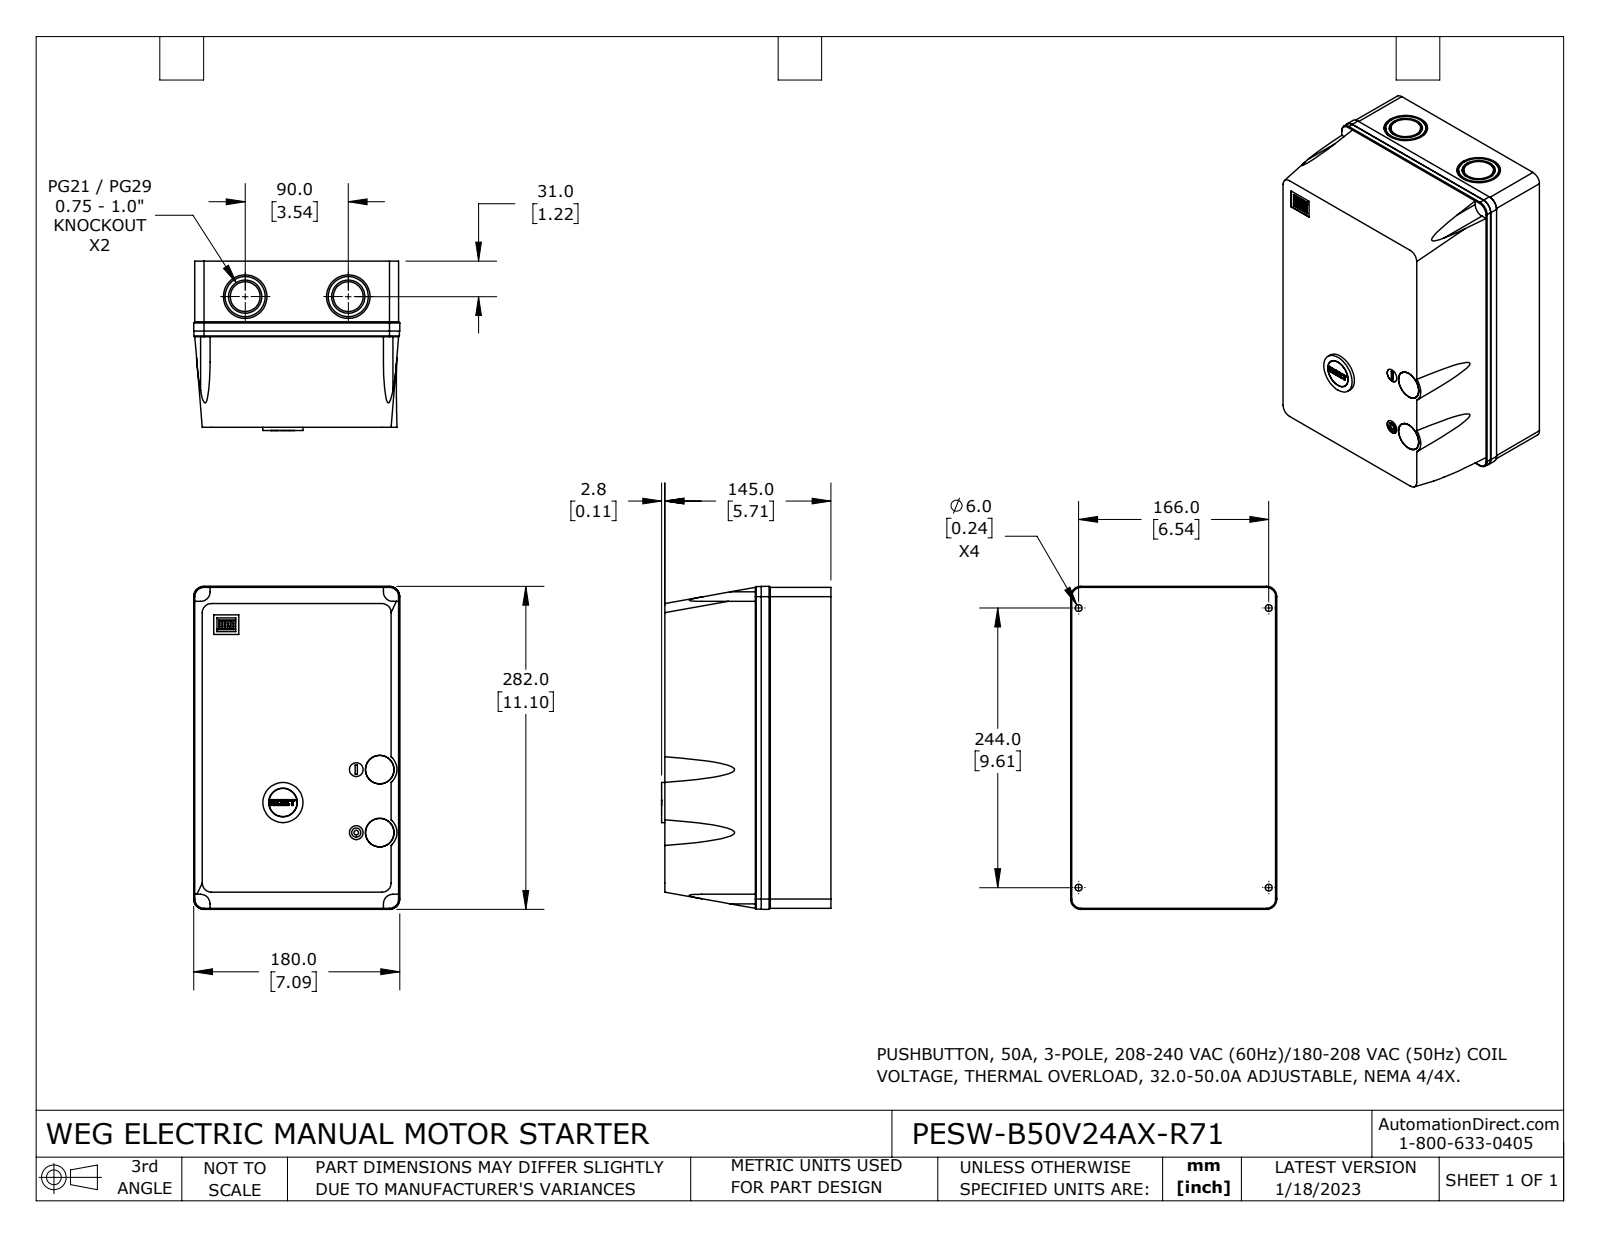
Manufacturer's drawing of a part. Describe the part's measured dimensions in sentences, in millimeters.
The part is named "PESW-B50V24AX-R71". Its 3-D file was written by "SolidWorks 2021 (CONFIG_CONTROL_DESIGN)". It is 3 solids with 286 faces: 130 planar, 144 cylindrical and 12 other. Overall it measures 282 by 180 by 147.9 millimeters. Its volume is 7 014 000 cubic millimeters and its surface area 232 257 square millimeters. Round holes: 4 of diameter 6, 3 of diameter 25, 2 of diameter 12, 2 of diameter 29, 2 of diameter 38, 1 of diameter 4, 1 of diameter 30.5. Round bosses or shafts: 3 of diameter 35, 2 of diameter 26, 2 of diameter 24.8, 1 of diameter 30.3, 1 of diameter 24.6, 1 of diameter 14, 1 of diameter 8. Partial cylindrical surfaces (rounded edges, fillets, slot ends): 34 of radius 0.1, 4 of radius 8, 4 of radius 8.3, 4 of radius 8.7, 4 of radius 9, 1 of radius 1.6. The main face-to-face distances are 145, 178, 280, 1, 0.7, 179, 179.7, 178.7, 281, 180. The hole center spacings are 20.5, 55, 58.7, 166, 244, 295.11, 49.14, 57.14.
